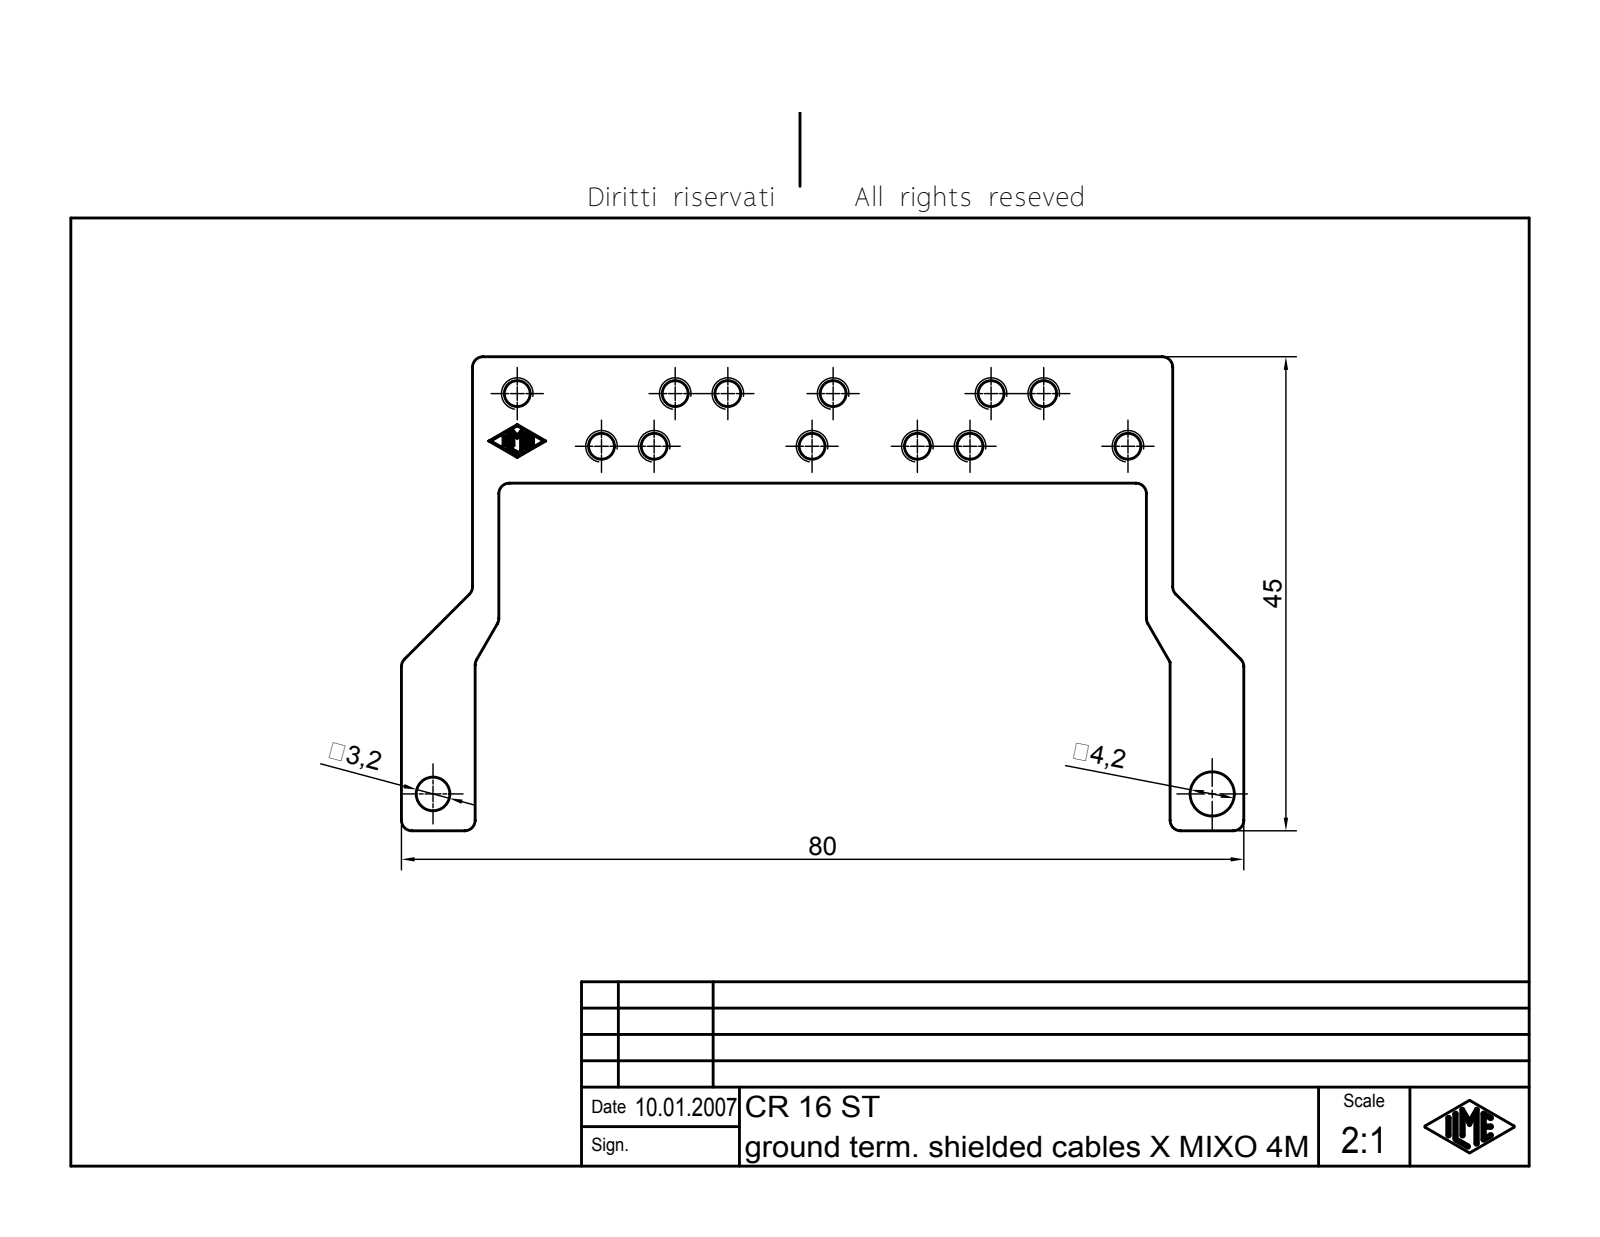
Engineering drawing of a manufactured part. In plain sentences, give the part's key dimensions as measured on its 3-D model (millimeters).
The part is named "CR 16 ST". Its 3-D file was written by "Autodesk Inventor 7 (AUTOMOTIVE_DESIGN)". It is 1 solid with 127 faces: 55 planar, 48 cylindrical and 24 other. Overall it measures 80 by 45 by 2 millimeters. Its volume is 2 127 cubic millimeters and its surface area 2 972 square millimeters. Round holes: 1 of diameter 3.2, 1 of diameter 4.2. Partial cylindrical surfaces (rounded edges, fillets, slot ends): 15 of radius 1, 14 of radius 0.1. The main face-to-face distances are 2, 12, 66.25, 6.75, 7, 73, 73.25, 2.5, 9.25, 70.75. The hole center spacings are 74.
